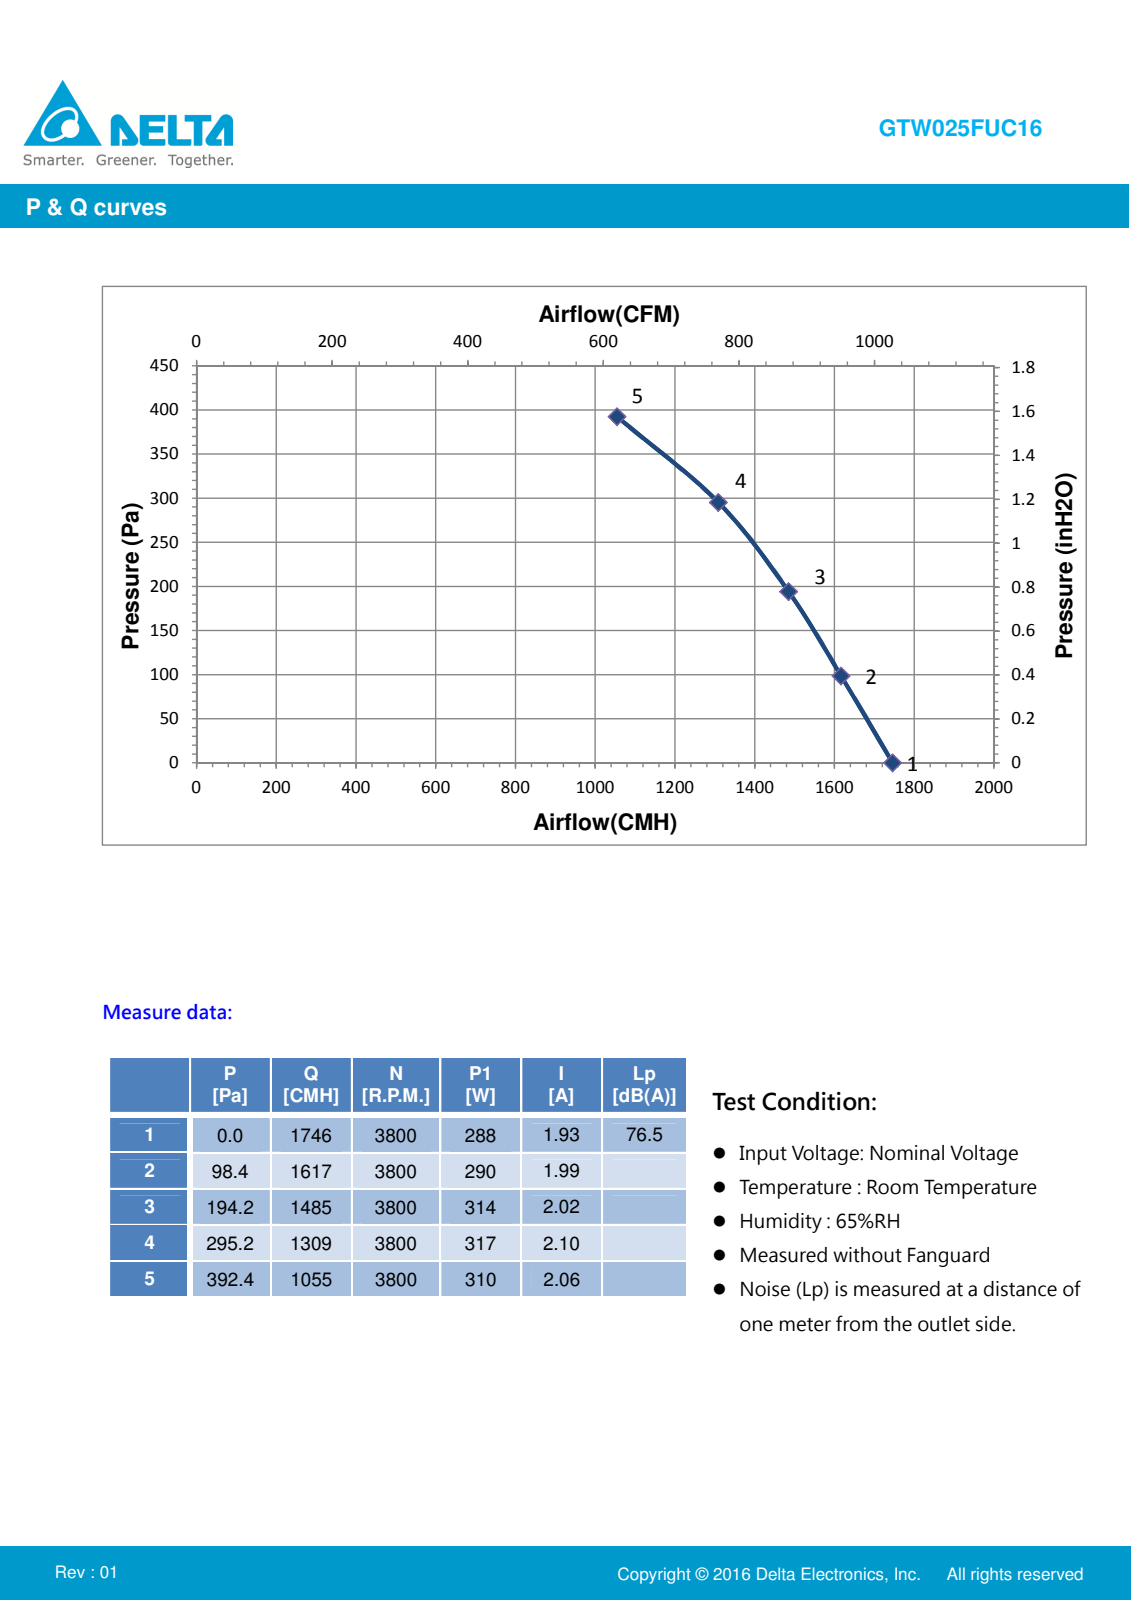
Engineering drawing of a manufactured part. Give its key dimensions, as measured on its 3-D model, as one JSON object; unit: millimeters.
{"part_name": "PRT0020_AF0; PRT0021; ASM0010_ASM; ASM0009_ASM (+5 more)", "step_written_by": "PRO/ENGINEER BY PARAMETRIC TECHNOLOGY CORPORATION, 2007310 (CONFIG_CONTROL_DESIGN)", "units": "millimeters", "bodies": {"solids": 5, "faces": 1037, "planar": 340, "cylindrical": 387, "other": 310}, "overall_size": [312.93, 312.93, 180.52], "volume_mm3": 2245000, "surface_area_mm2": 548732, "round_holes": [[6.5, 8], [2.5, 4], [3, 4], [4, 4], [7.5, 2], [9.06, 2], [152, 1], [180, 1], [245, 1]], "round_bosses_or_shafts": [[14.5, 2], [10, 2], [9, 2], [146, 1]], "partial_cylinders_radius": [[1, 182], [2, 6], [7, 4], [7.5, 4], [75, 1], [85, 1], [126.5, 1], [126.5, 1]], "face_to_face_distances": [118, 8, 253, 75.6, 4, 42.4, 249, 110, 3.5, 31.7], "hole_center_spacings": [62.76, 82, 151.52, 213.1, 65.08, 106.3, 106.31, 115.96]}
